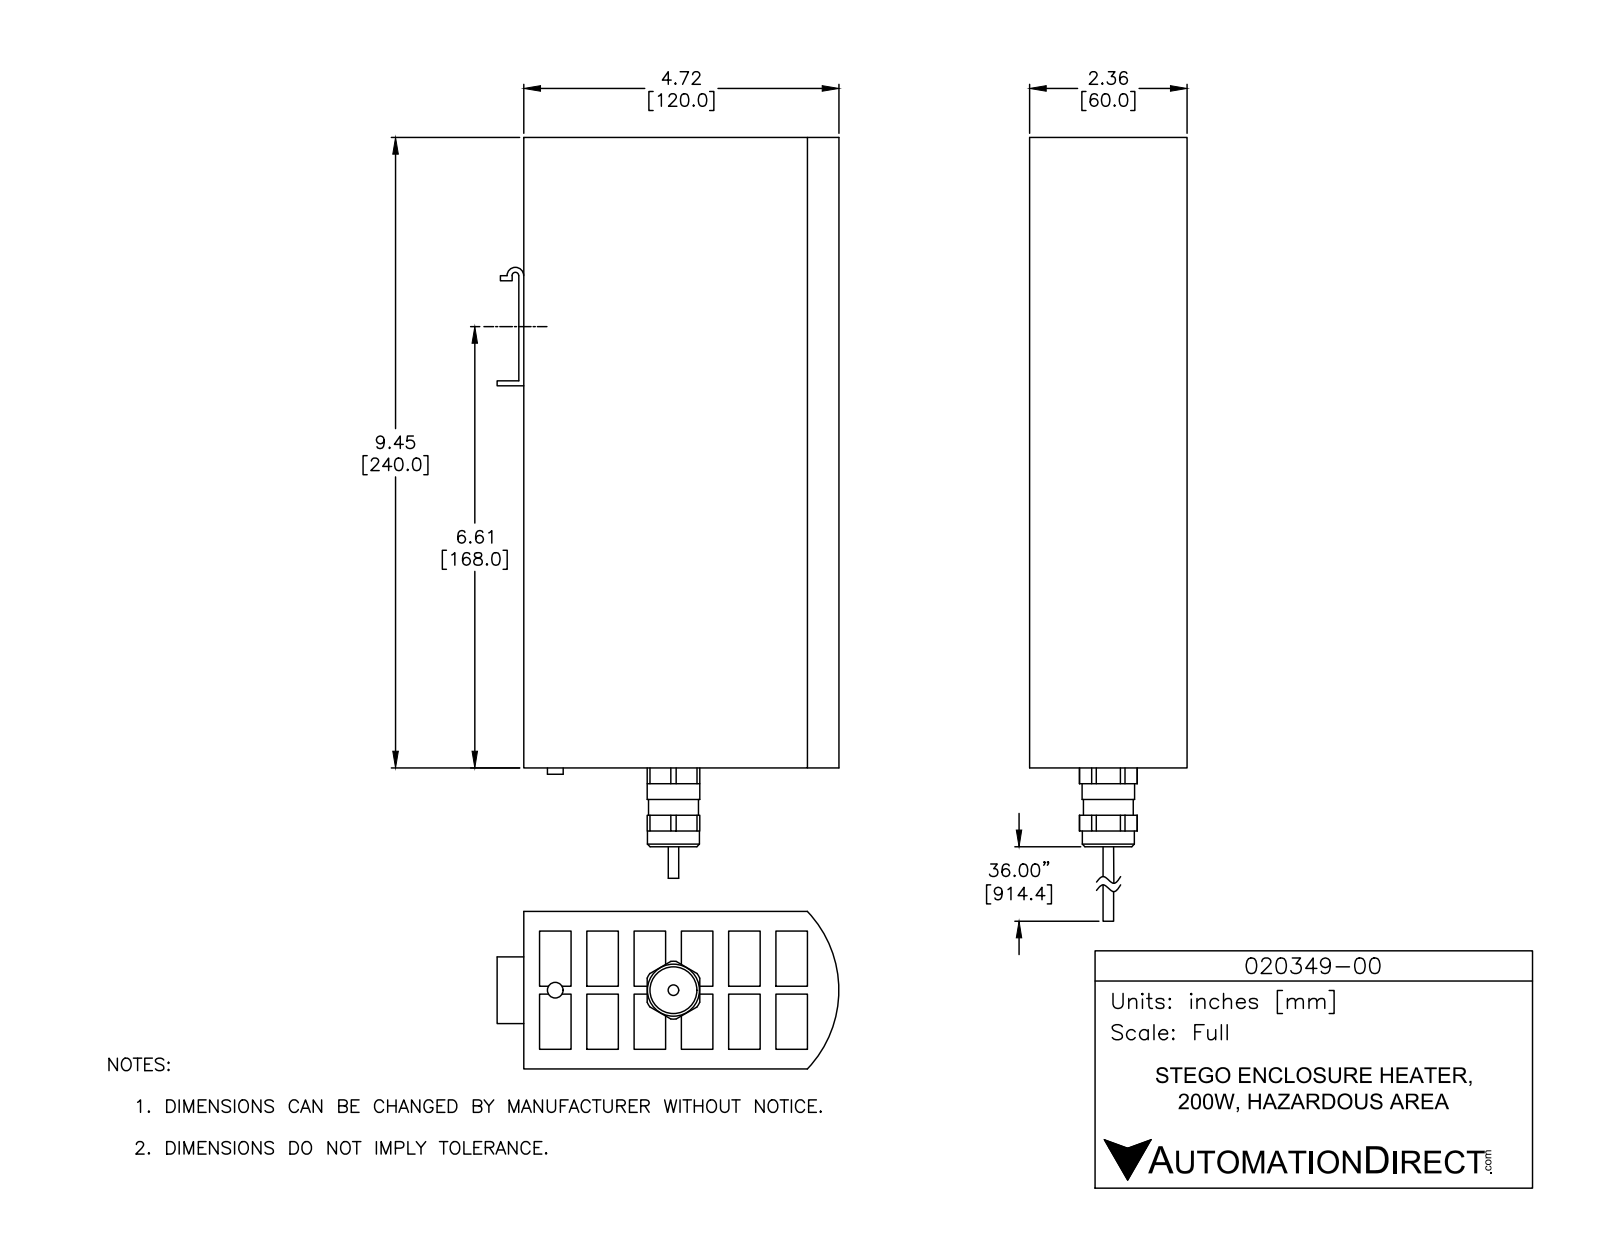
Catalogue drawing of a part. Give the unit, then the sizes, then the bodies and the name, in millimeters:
Units: millimetres
Overall size (bounding box): 282 × 130.16 × 60
Round bosses / shafts (diameter × count): ⌀20 ×1, ⌀19.8 ×1, ⌀19 ×1, ⌀6 ×1, ⌀4 ×1
Partial cylindrical surfaces — rounded edges, fillets, slot ends (radius × count): R1.27 ×1, R3.17 ×1, R11 ×1, R43.5 ×1
Main face-to-face distances: 18, 36, 24, 54, 6, 12, 60, 72, 30, 7.5
Volume: 978 866 mm³ · Surface area: 280 574 mm²
Bodies: 1 solid, 124 faces (97 planar, 25 cylindrical, 2 other)
Part name (STEP PRODUCT): PRODUCT_NAME_1
STEP written by: ACIS (AUTOMOTIVE_DESIGN_CC2)
